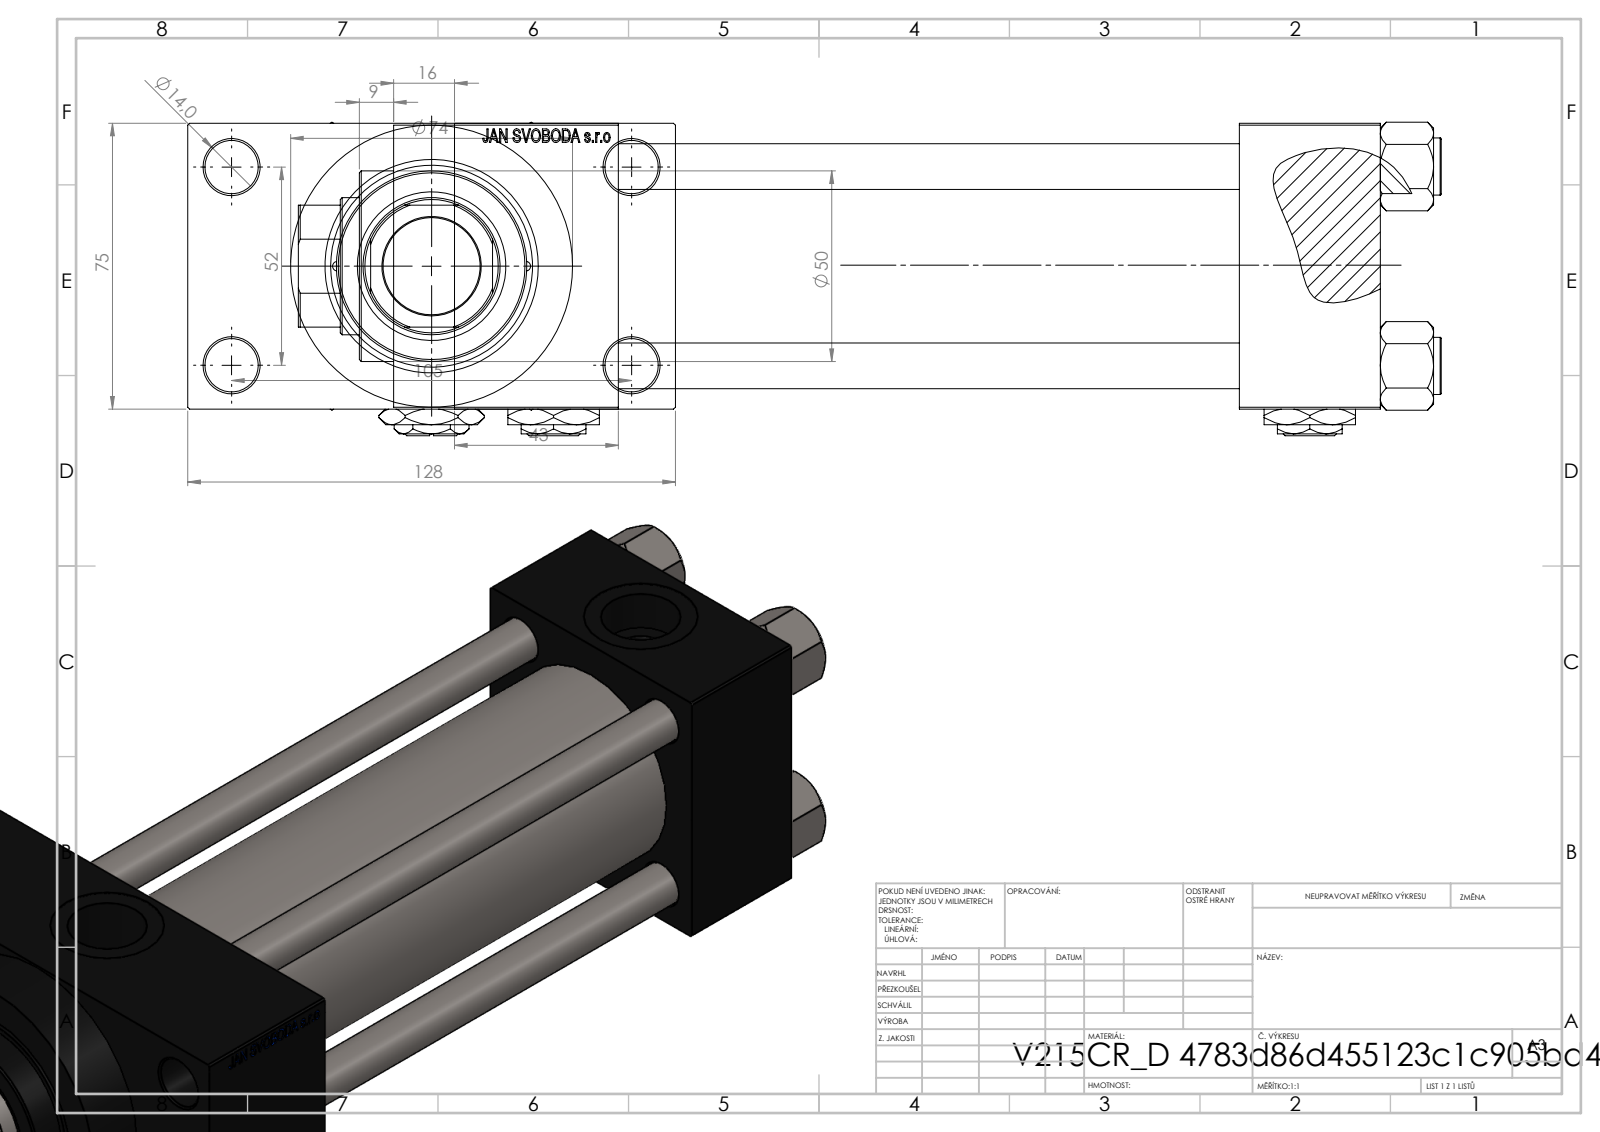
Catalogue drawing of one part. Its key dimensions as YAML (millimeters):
part_name: "Zatka_pro_OIL_PORT; NUT_M5_D; V215CR_VCP_D; V215CR_D_TYCINKA (+2 more)"
step_written_by: "SolidWorks 2019 (CONFIG_CONTROL_DESIGN)"
units: millimeters
bodies: {solids: 13, faces: 1215, planar: 549, cylindrical: 104, other: 562}
overall_size: [300, 128, 82.27]
volume: 1029000
surface_area: 240650
round_holes:
  - {diameter: 12, count: 4}
  - {diameter: 14, count: 4}
  - {diameter: 2.5, count: 2}
  - {diameter: 7, count: 2}
  - {diameter: 20.96, count: 2}
  - {diameter: 30, count: 2}
  - {diameter: 25.5, count: 1}
  - {diameter: 36, count: 1}
  - {diameter: 39, count: 1}
  - {diameter: 41, count: 1}
  - {diameter: 53, count: 1}
round_bosses_or_shafts:
  - {diameter: 15, count: 4}
  - {diameter: 74, count: 1}
  - {diameter: 56, count: 1}
  - {diameter: 50, count: 1}
partial_cylinders:
  - {radius: 17.5, count: 1}
face_to_face_distances: [75, 163, 37, 200, 26.5, 101.5, 243, 43, 206, 128]
hole_center_spacings: [26.19, 26.35, 36.98, 38.03, 52.3, 57.22, 58.43, 58.59]
